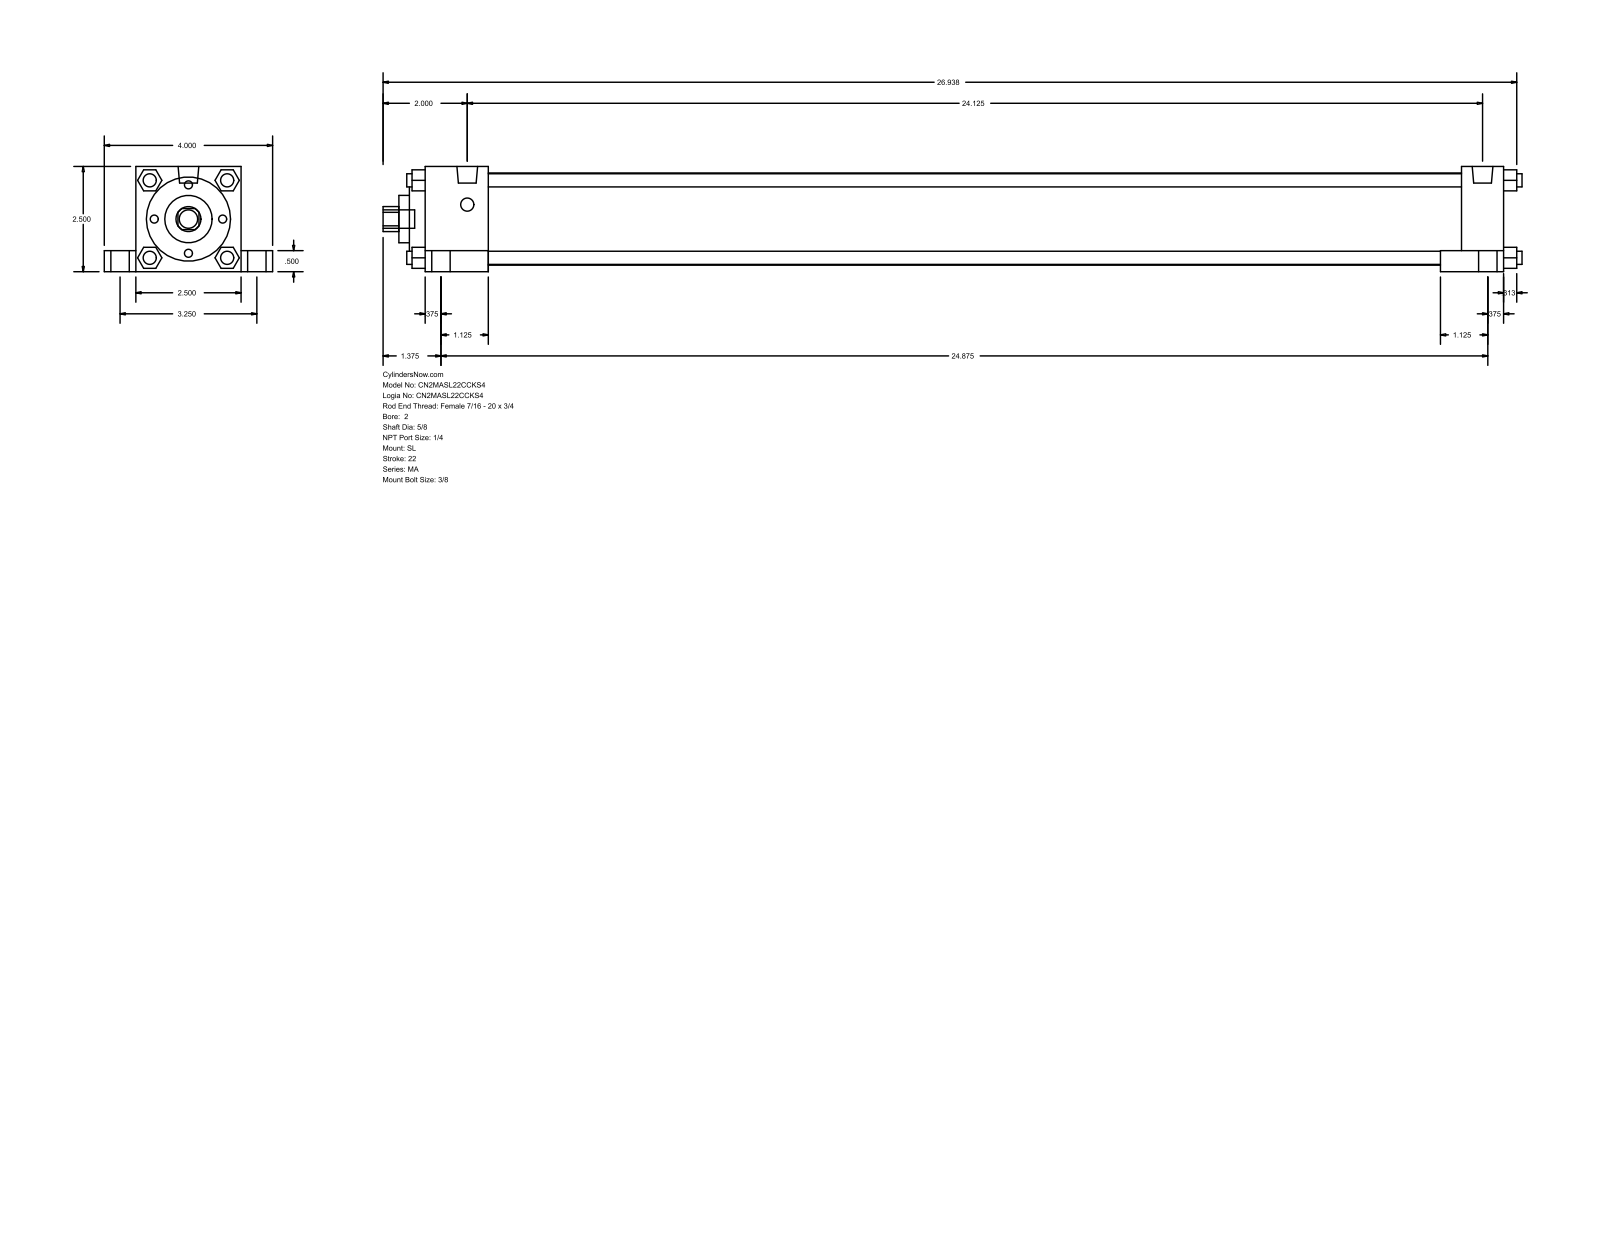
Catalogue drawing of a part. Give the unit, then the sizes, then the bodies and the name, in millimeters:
Units: millimetres
Overall size (bounding box): 687.39 × 101.6 × 63.5
Round holes (diameter × count): ⌀15.88 ×1, ⌀28.57 ×1, ⌀50.8 ×1, ⌀55.63 ×1
Round bosses / shafts (diameter × count): ⌀7.94 ×8, ⌀11.11 ×5, ⌀17.46 ×4, ⌀12.49 ×2
Partial cylindrical surfaces — rounded edges, fillets, slot ends (radius × count): R7.54 ×1
Main face-to-face distances: 63.5, 12.7, 9.52, 19.05, 82.55, 38.1, 50.8, 650.87, 612.77, 625.48
Bodies: 0 solids, 150 faces (113 planar, 37 cylindrical, 0 other)
Part name (STEP PRODUCT): MA_SL__0200_0.625
STEP written by: GSSL Pune (CONFIG_CONTROL_DESIGN)
